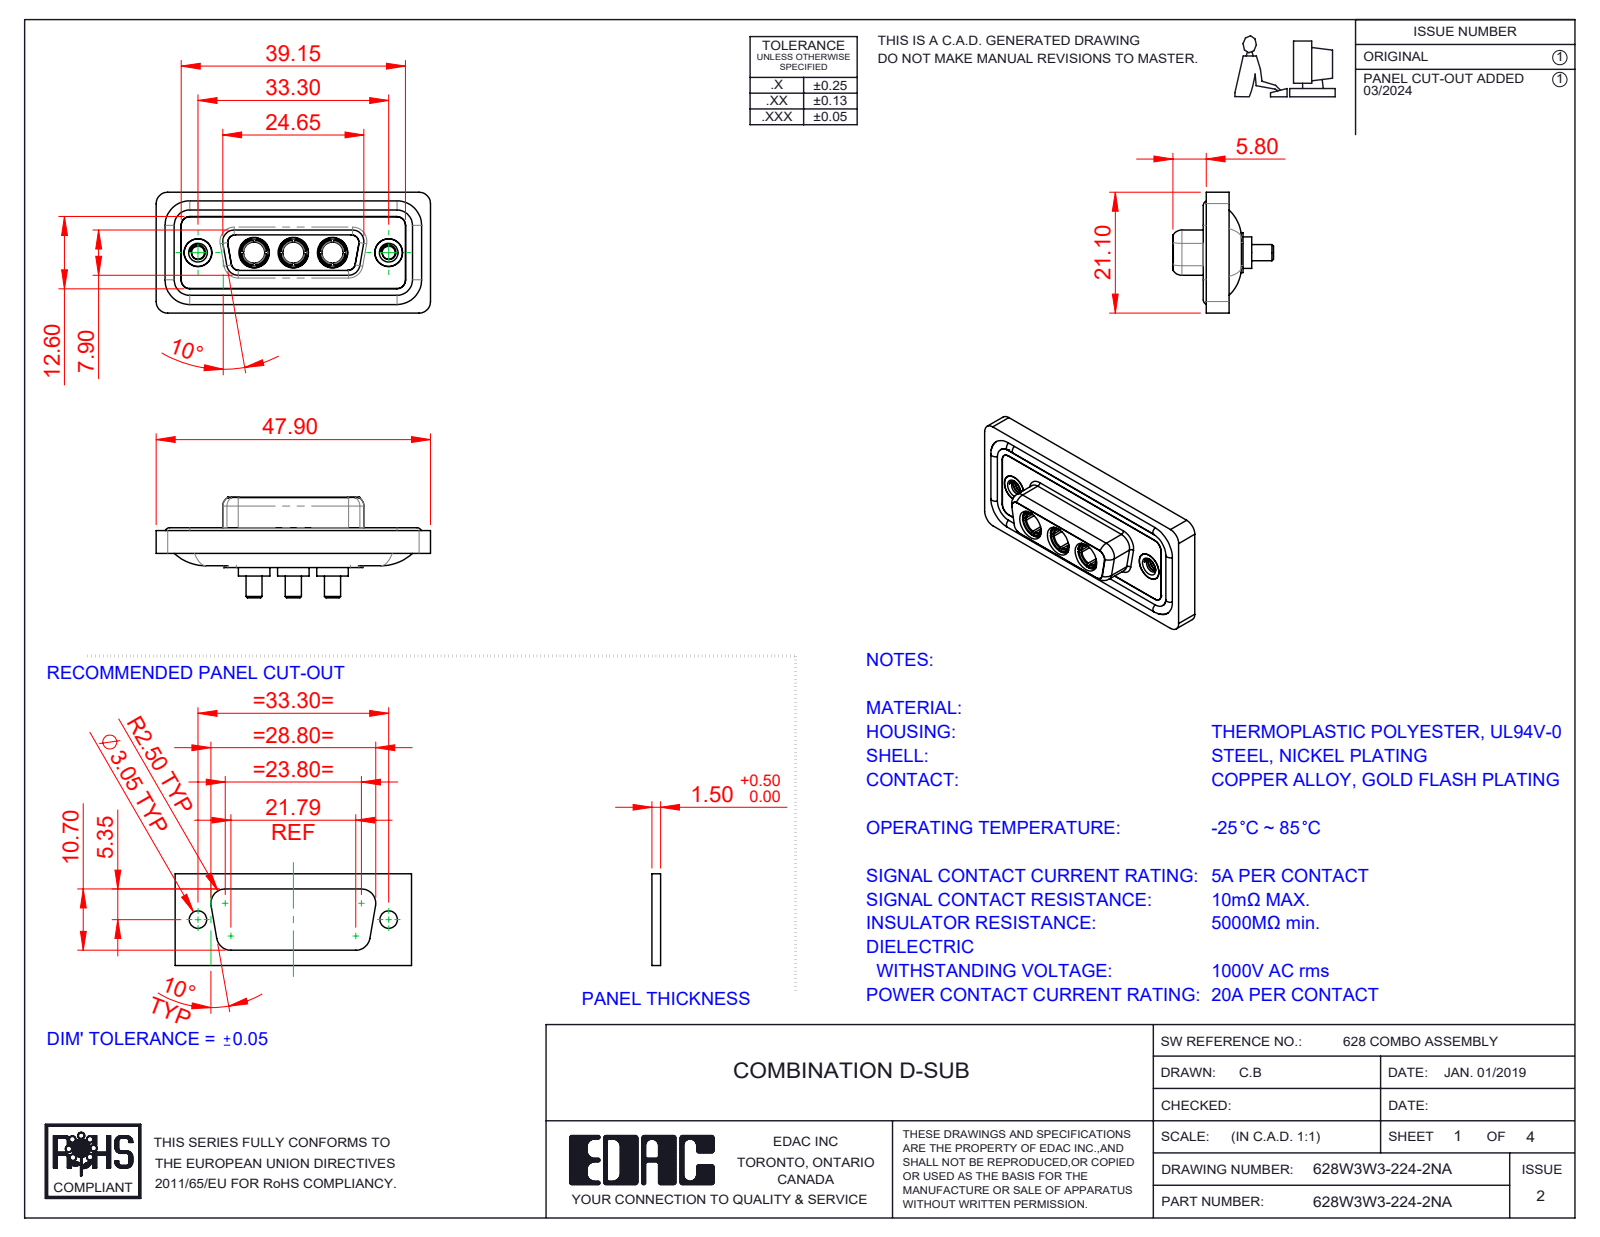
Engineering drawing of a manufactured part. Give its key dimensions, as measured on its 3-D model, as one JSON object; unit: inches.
{"part_name": "628Combo Shell Front_15 Contacts; Power Socket_20A S; 628Combo Shell Rear_15 Contacts; 628Combo Housing_3W3 (+3 more)", "step_written_by": "SolidWorks 2023 (CONFIG_CONTROL_DESIGN)", "units": "inches", "bodies": {"solids": 13, "faces": 606, "planar": 192, "cylindrical": 259, "other": 155}, "overall_size": [1.886, 0.831, 0.691], "volume_in3": 0.368, "surface_area_in2": 15.09, "round_holes": [[0.191, 5], [0.146, 3], [0.209, 3], [0.089, 2], [0.157, 2], [0.159, 2], [0.197, 2]], "round_bosses_or_shafts": [[0.063, 4], [0.217, 3], [0.205, 3], [0.195, 3], [0.187, 3], [0.148, 3], [0.11, 3], [0.195, 2]], "partial_cylinders_radius": [[0.059, 22], [0.079, 20], [0.053, 12], [0.063, 8], [0.01, 4], [0.02, 4], [0.024, 4], [0.026, 4]], "face_to_face_distances": [0.016, 0.071, 0.063, 0.02, 0.293, 0.043, 0.114, 0.222, 0.278, 0.26], "hole_center_spacings": [0.27, 0.386, 0.656, 0.925, 0.539, 1.311]}
